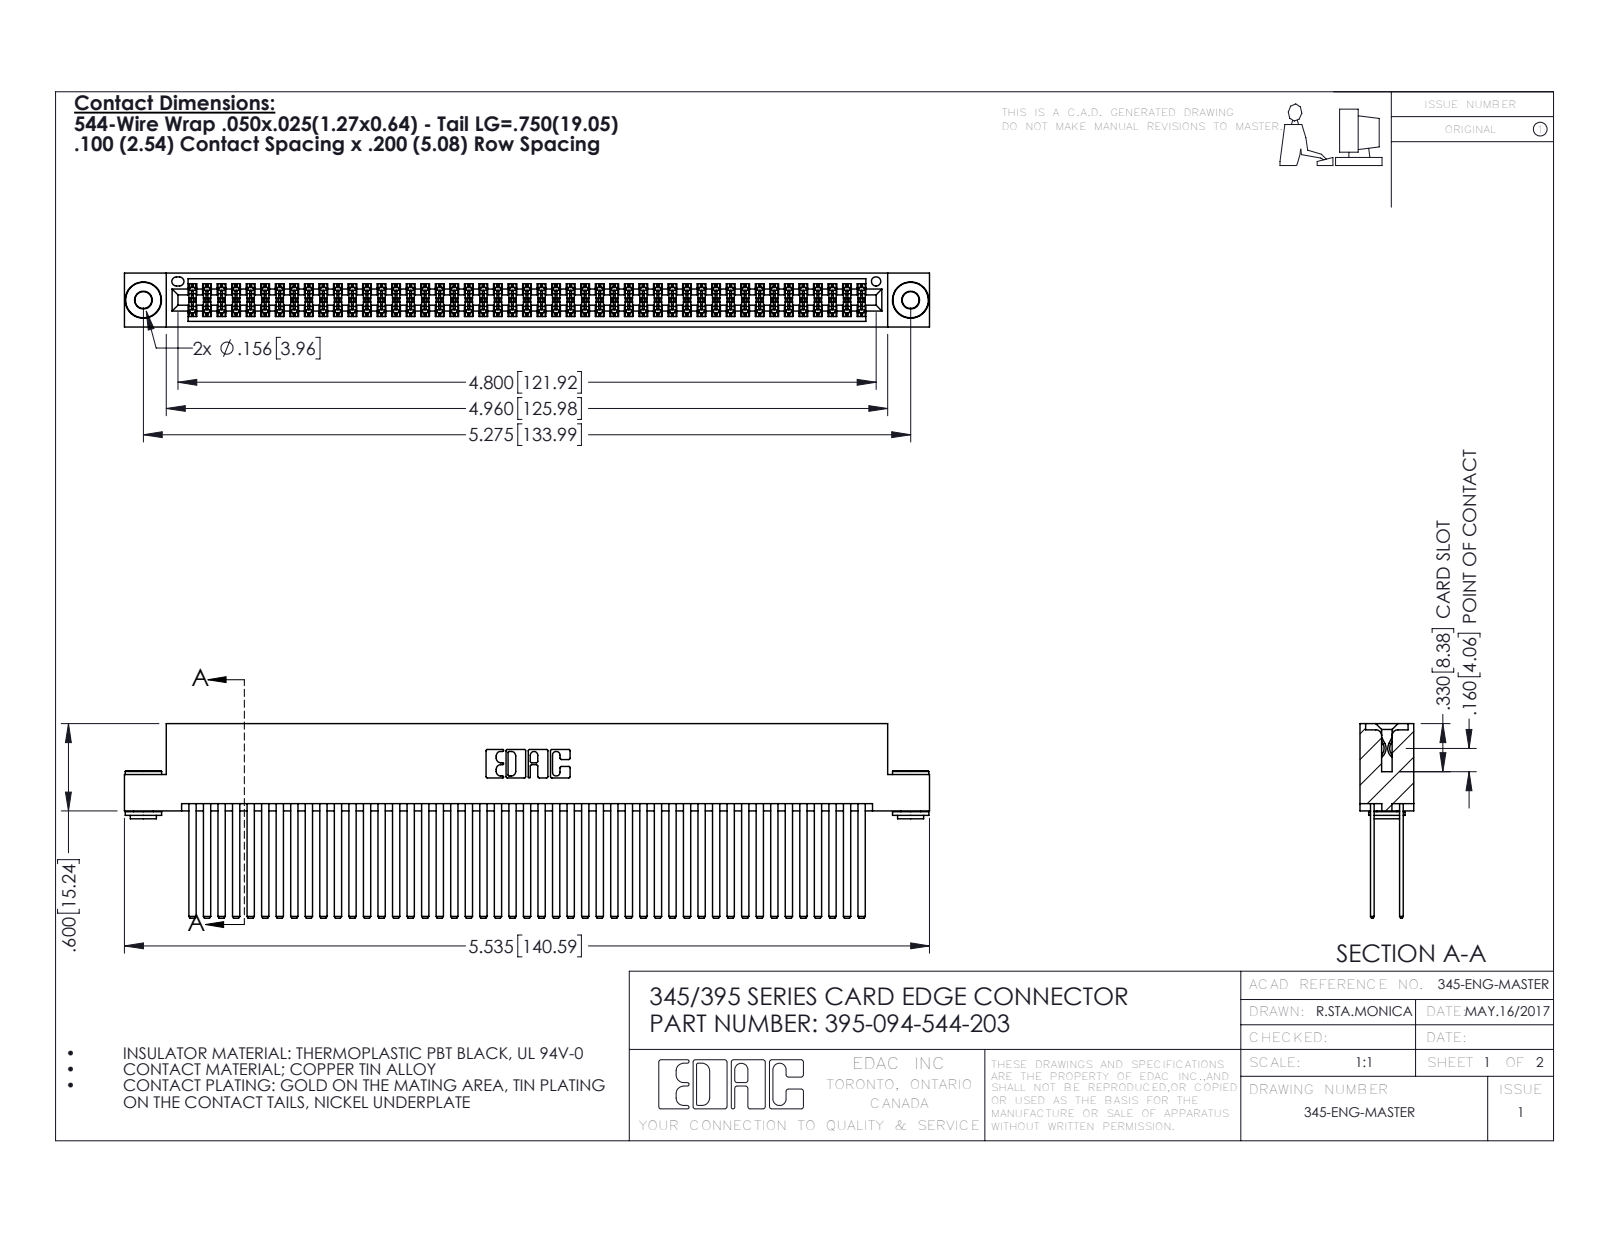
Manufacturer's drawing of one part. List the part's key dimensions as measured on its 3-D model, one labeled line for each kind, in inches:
Part name (STEP PRODUCT): 345 Part_Flush Mounting Lugs - 0.156 Dia-TH; 345-292-001_345-293-144; 345-250-002_345-250-002-102; 395-094-544-203
STEP written by: SolidWorks 2016 (CONFIG_CONTROL_DESIGN)
Units: inches
Bodies: 97 solids, 4300 faces (2816 planar, 1476 cylindrical, 8 other)
Overall size (bounding box): 5.535 × 1.337 × 0.37
Volume: 0.918 in³ · Surface area: 40.91 in²
Round holes (diameter × count): ⌀0.116 ×2, ⌀0.156 ×2, ⌀0.064 ×1
Round bosses / shafts (diameter × count): ⌀0.25 ×2, ⌀0.18 ×2, ⌀0.136 ×2
Partial cylindrical surfaces — rounded edges, fillets, slot ends (radius × count): R0.006 ×141, R0.01 ×22, R0.007 ×6, R0.031 ×6, R0.026 ×3, R0.014 ×2, R0.019 ×2, R0.022 ×2
Main face-to-face distances: 0.2, 0.025, 0.072, 0.098, 0.272, 0.298, 0.225, 0.175, 0.37, 0.05
Hole centre spacings: 0.27, 5.039, 5.275
